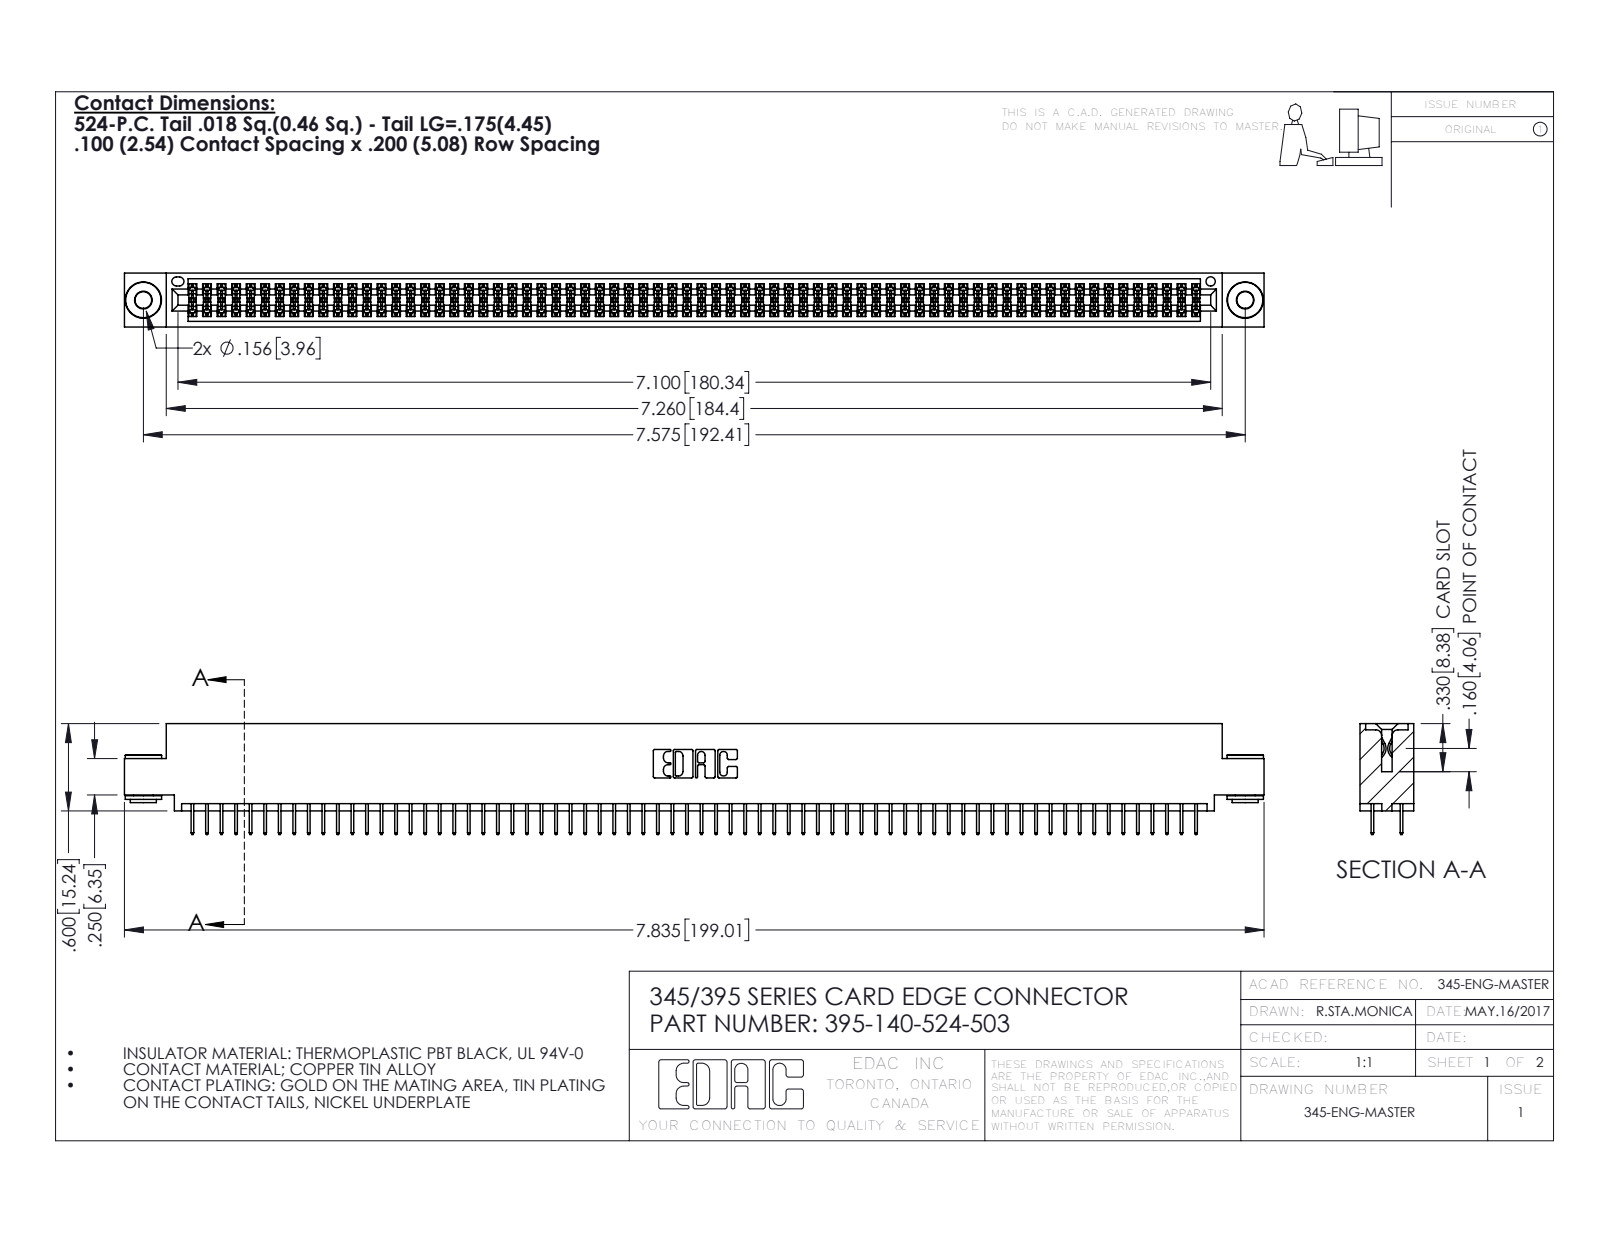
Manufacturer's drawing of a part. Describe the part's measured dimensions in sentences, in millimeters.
The part is named "345 Part_0.110 Offset - 0.156 Dia-TH; 345-292-001_345-293-124; 395-140-524-503; 345-250-002_345-250-002-102". Its 3-D file was written by "SolidWorks 2016 (CONFIG_CONTROL_DESIGN)". It is 143 solids with 7728 faces: 5554 planar, 2166 cylindrical and 8 other. Overall it measures 199 by 19.4 by 9.4 millimeters. Its volume is 19 320 cubic millimeters and its surface area 28 850 square millimeters. Round holes: 2 of diameter 2.9, 2 of diameter 4, 1 of diameter 1.6. Round bosses or shafts: 2 of diameter 6.4, 2 of diameter 4.6, 2 of diameter 3.5. Partial cylindrical surfaces (rounded edges, fillets, slot ends): 210 of radius 0.2, 22 of radius 0.3, 6 of radius 0.2, 6 of radius 0.8, 3 of radius 0.7, 2 of radius 0.4, 2 of radius 0.5, 2 of radius 0.6. The main face-to-face distances are 1.8, 7.6, 5.1, 9.4, 0.6, 2.5, 6.9, 5.7, 1.8, 4.4. The hole center spacings are 6.9, 186.4, 192.4.
